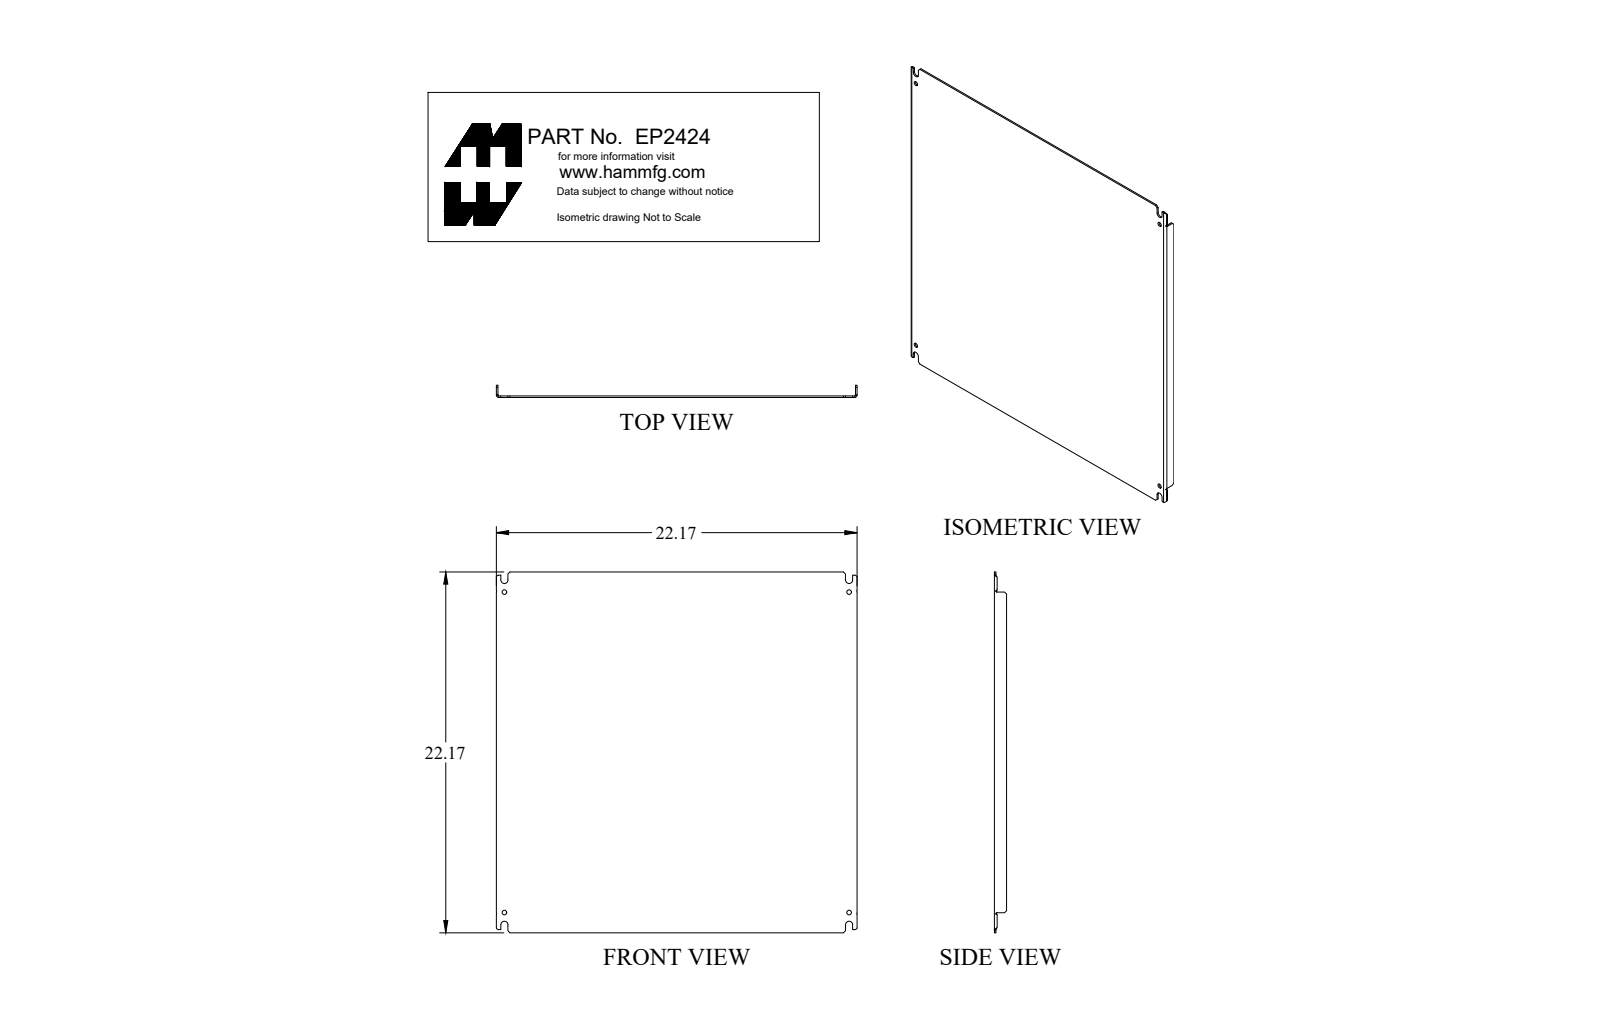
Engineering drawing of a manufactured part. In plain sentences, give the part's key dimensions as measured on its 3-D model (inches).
The part is named "EP2424". Its 3-D file was written by "SolidWorks 2018 (AUTOMOTIVE_DESIGN)". It is 1 solid with 84 faces: 50 planar, 26 cylindrical and 8 other. Overall it measures 22.17 by 22.17 by 0.75 inches. Its volume is 48.84 cubic inches and its surface area 1 037 square inches. Round holes: 4 of diameter 0.281. Partial cylindrical surfaces (rounded edges, fillets, slot ends): 4 of radius 0.219, 2 of radius 0.048, 2 of radius 0.062, 2 of radius 0.143. The main face-to-face distances are 0.095, 22.075, 22.17, 21.98, 0.75, 0.655, 0.171, 0.076, 0.579, 1.235. The hole center spacings are 19.688, 21.188, 28.923.
